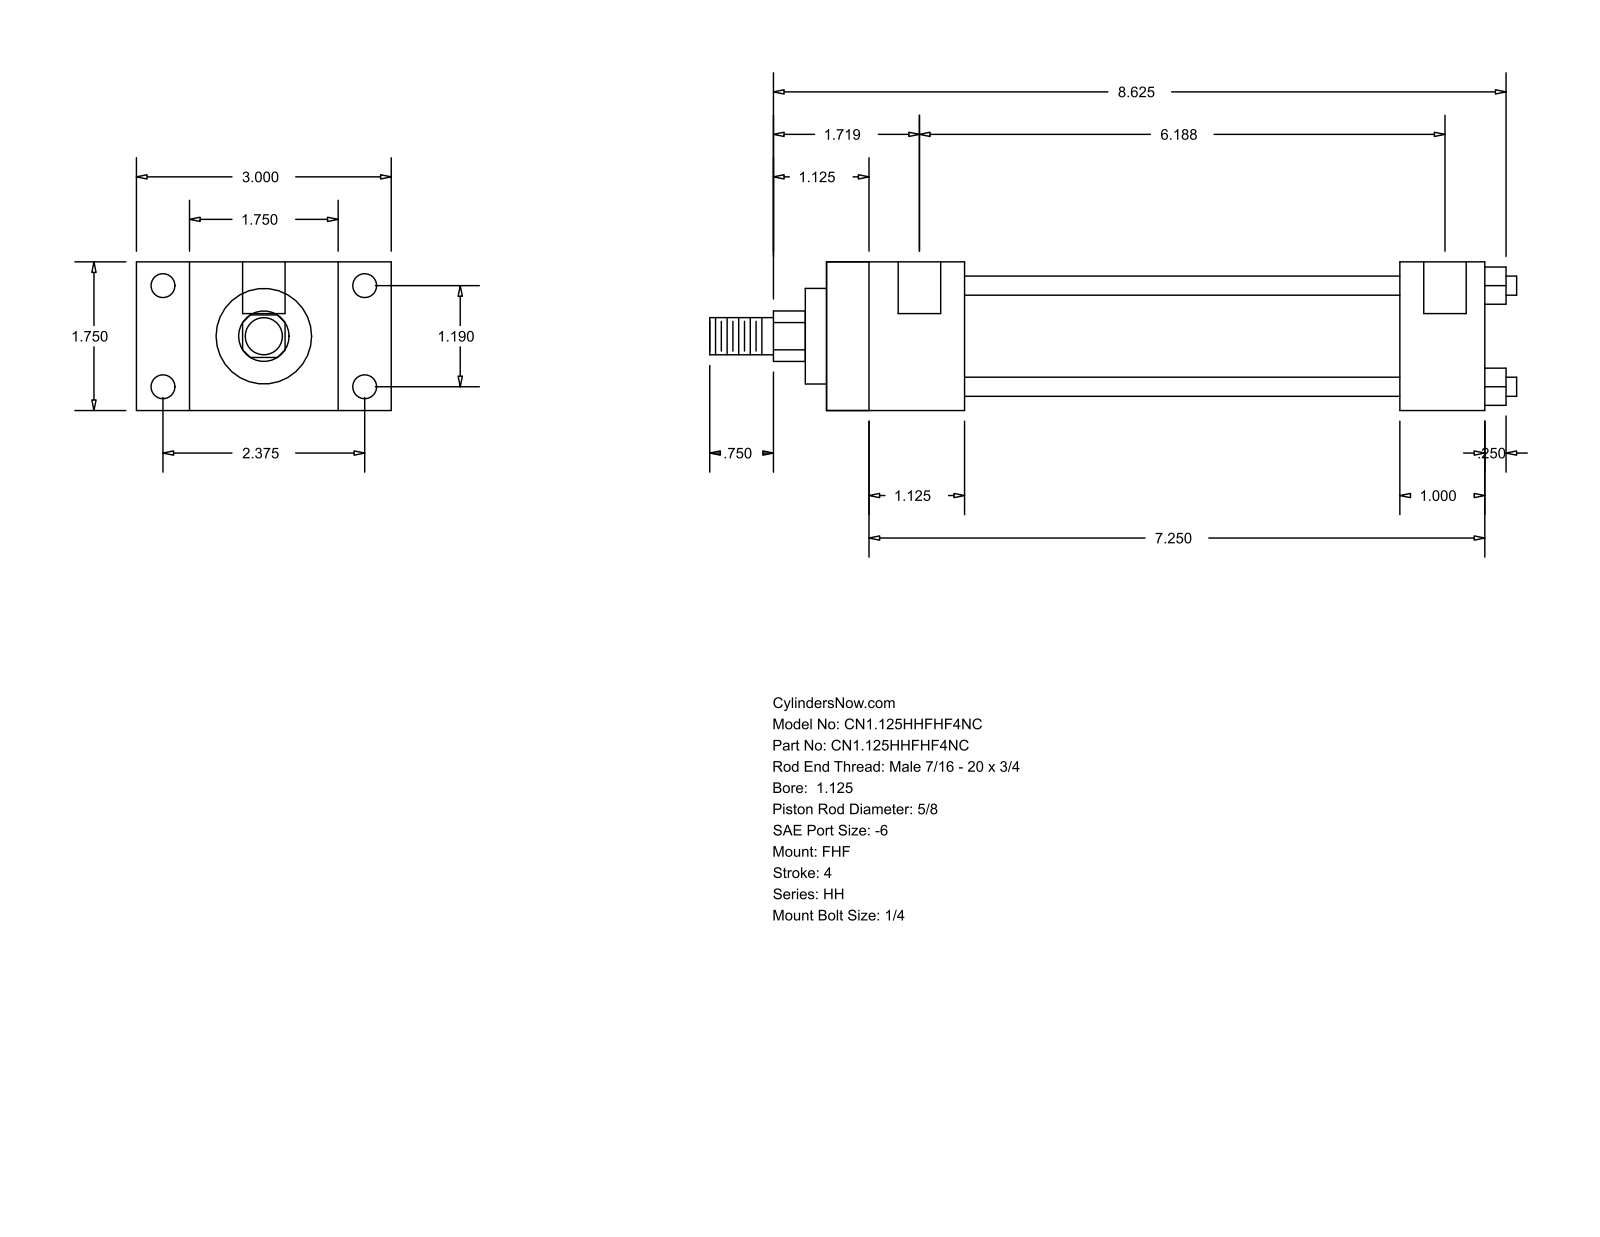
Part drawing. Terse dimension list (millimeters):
name: HH_FHF__0112_0.625
written by: GSSL Pune (CONFIG_CONTROL_DESIGN)
unit: mm
bodies: 0 solids, 88 faces (60 planar, 28 cylindrical, 0 other)
size: 241.3 × 76.2 × 44.45
holes: 4× ⌀5.56, 4× ⌀7.14, 2× ⌀12.7
bosses: 4× ⌀5.71, 1× ⌀34.92, 1× ⌀28.57, 1× ⌀15.88, 1× ⌀11.11
rounds: 1× R7.54
face distances: 44.46, 15.87, 60.33, 41.27, 76.2, 196.84, 155.57, 25.4, 171.44, 130.17
hole spacings: 30.22, 60.32, 67.47, 153.99, 3.17, 157.16
